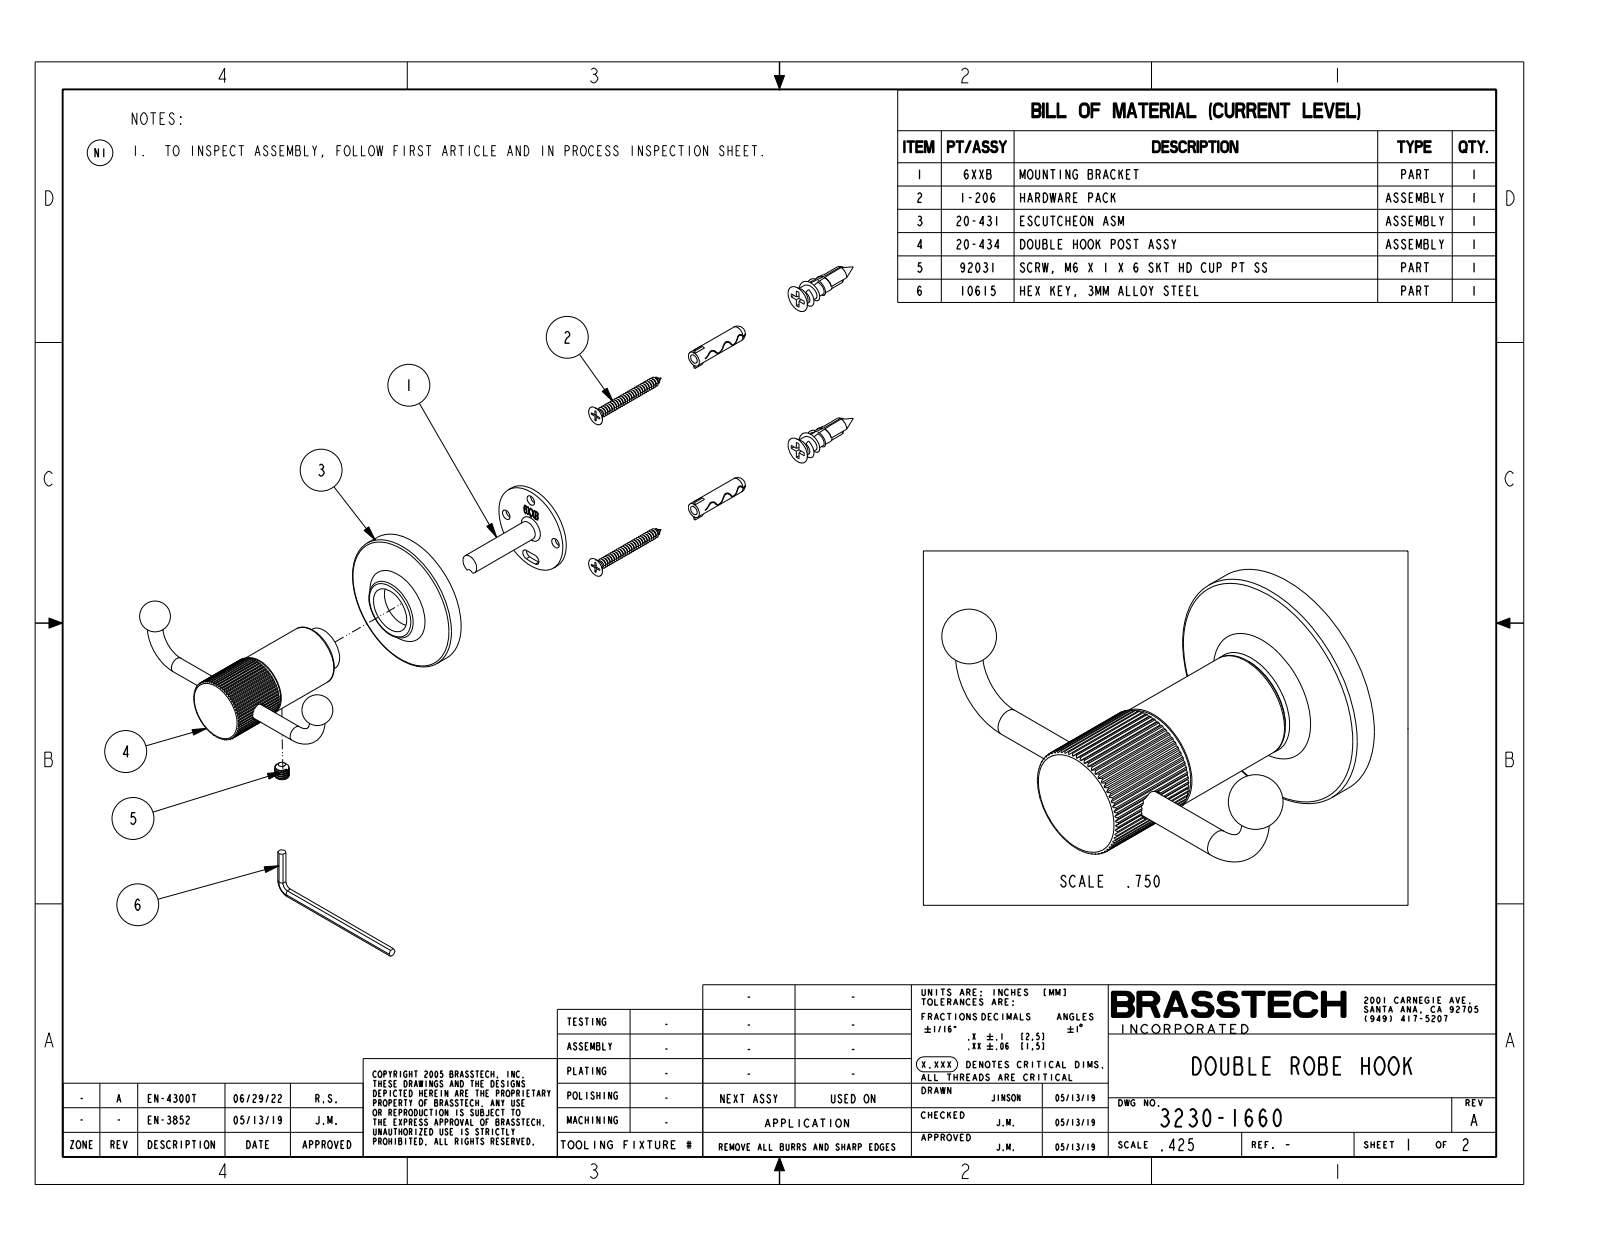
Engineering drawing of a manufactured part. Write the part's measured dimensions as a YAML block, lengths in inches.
part_name: "3230-1660"
step_written_by: "CREO PARAMETRIC BY PTC INC, 2019352 (CONFIG_CONTROL_DESIGN)"
units: inches
bodies: {solids: 1, faces: 260, planar: 156, cylindrical: 84, other: 20}
overall_size: [4.216, 2.74, 2.25]
volume: 3.404
surface_area: 22.13
round_bosses_or_shafts:
  - {diameter: 2.25, count: 1}
  - {diameter: 1, count: 1}
  - {diameter: 0.97, count: 1}
  - {diameter: 0.85, count: 1}
  - {diameter: 0.25, count: 1}
partial_cylinders:
  - {radius: 0.52, count: 1}
face_to_face_distances: [0.806, 2.74, 0.806, 0.805, 0.5, 2.24, 0.51, 2.23, 1.8, 1.3]
